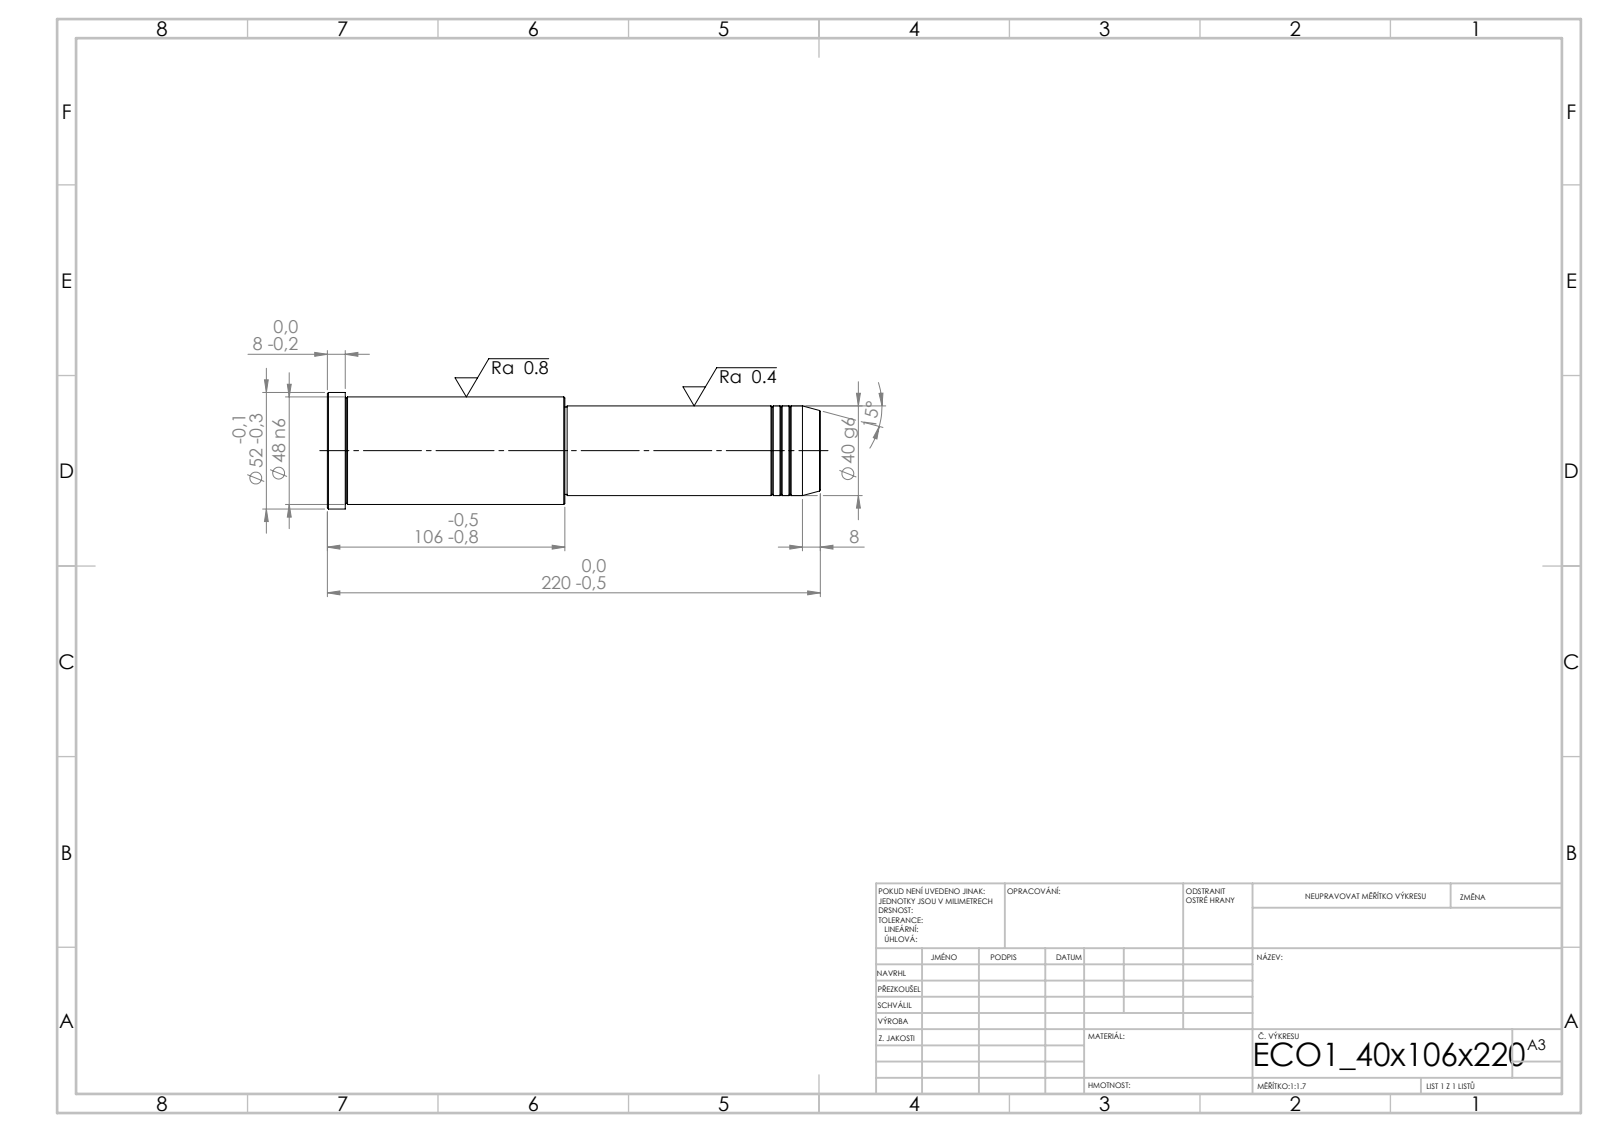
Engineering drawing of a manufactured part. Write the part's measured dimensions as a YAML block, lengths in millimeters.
step_written_by: "SolidWorks 2019 (CONFIG_CONTROL_DESIGN)"
units: millimeters
bodies: {solids: 1, faces: 43, planar: 5, cylindrical: 14, other: 24}
overall_size: [220, 52, 52]
volume: 336235
surface_area: 34687
round_bosses_or_shafts:
  - {diameter: 52, count: 1}
  - {diameter: 48, count: 1}
  - {diameter: 40, count: 1}
  - {diameter: 39, count: 1}
face_to_face_distances: [220, 114, 106, 212, 98, 8, 113, 1, 99, 107]
